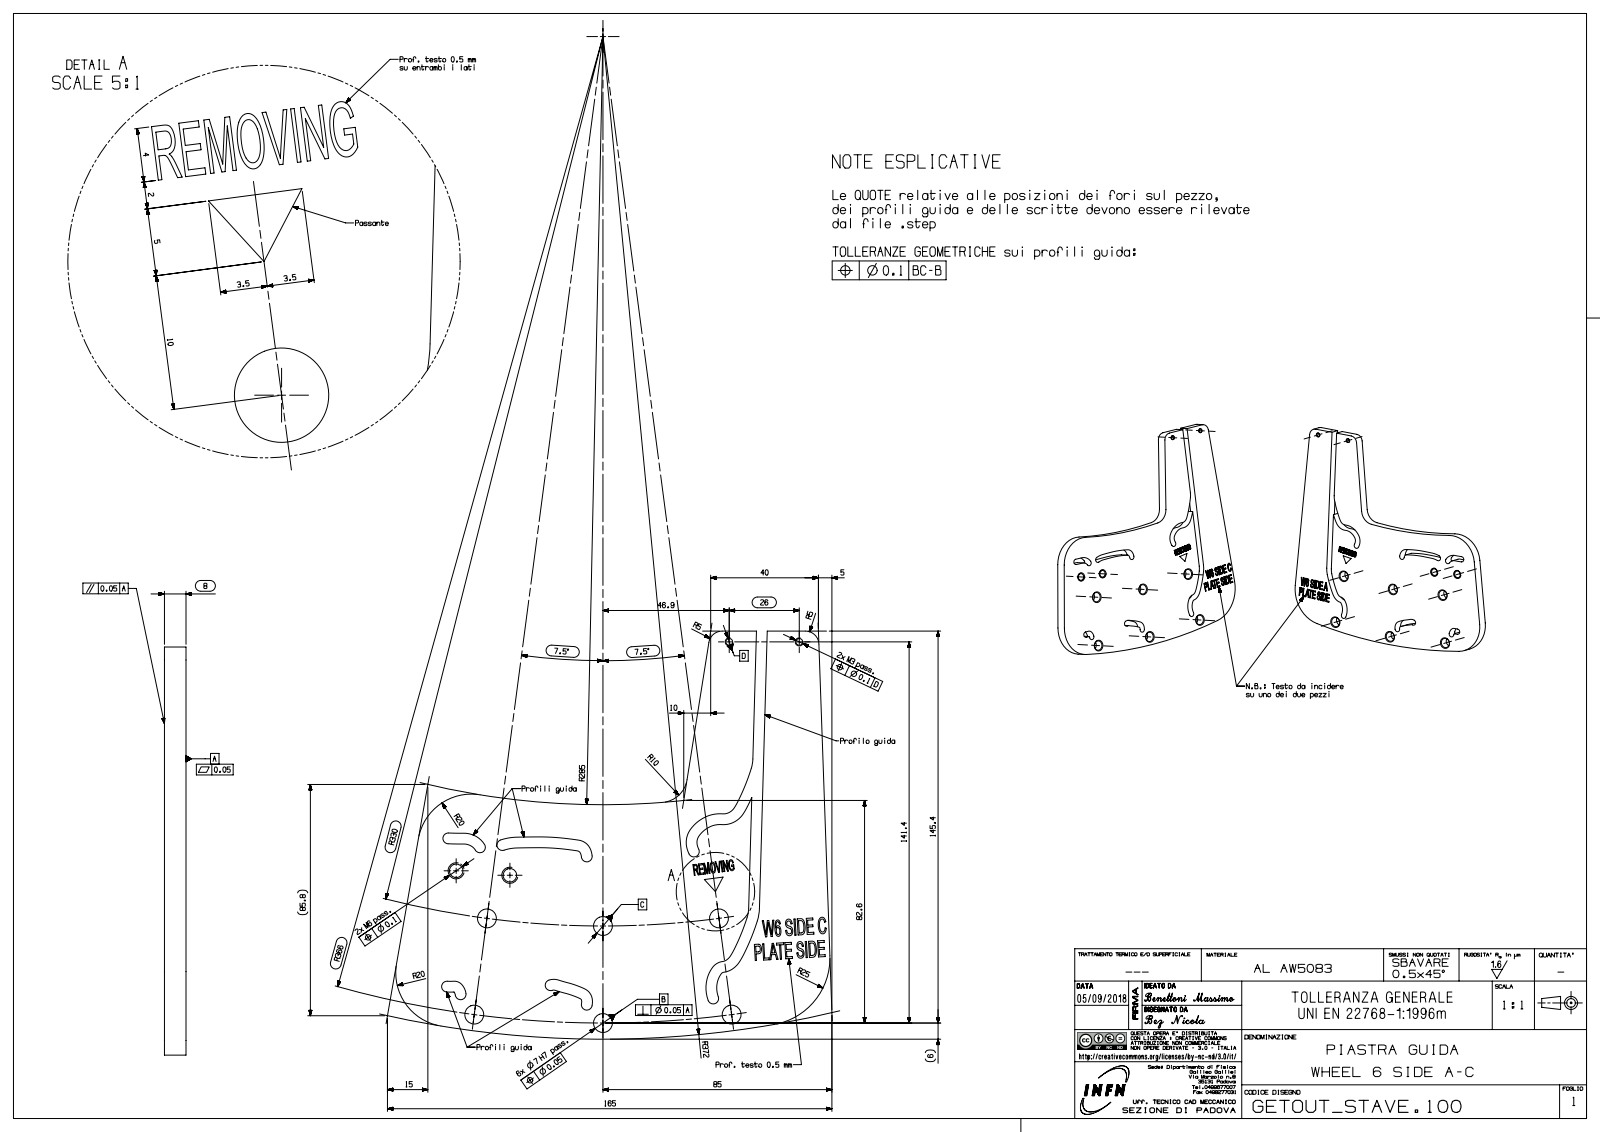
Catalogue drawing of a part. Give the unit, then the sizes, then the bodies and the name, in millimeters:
Units: millimetres
Overall size (bounding box): 192.26 × 143.84 × 8
Round holes (diameter × count): ⌀7 ×6, ⌀2.5 ×2, ⌀5 ×2
Partial cylindrical surfaces — rounded edges, fillets, slot ends (radius × count): R2 ×10, R5 ×2, R13 ×2, R20 ×2, R10 ×1, R17 ×1, R25 ×1, R285 ×1
Main face-to-face distances: 8, 4.04, 4.01, 0.5, 7.5, 7, 0.44, 1.22, 4.59, 4.15
Hole centre spacings: 57.99, 36, 43.17, 97.61, 18.14, 20.02, 21.03, 26
Volume: 117 775 mm³ · Surface area: 40 418 mm²
Bodies: 1 solid, 533 faces (375 planar, 31 cylindrical, 127 other)
Part name (STEP PRODUCT): bez8324385A6uze
STEP written by: SIEMENS PLM Software NX 12.0 (AUTOMOTIVE_DESIGN)
